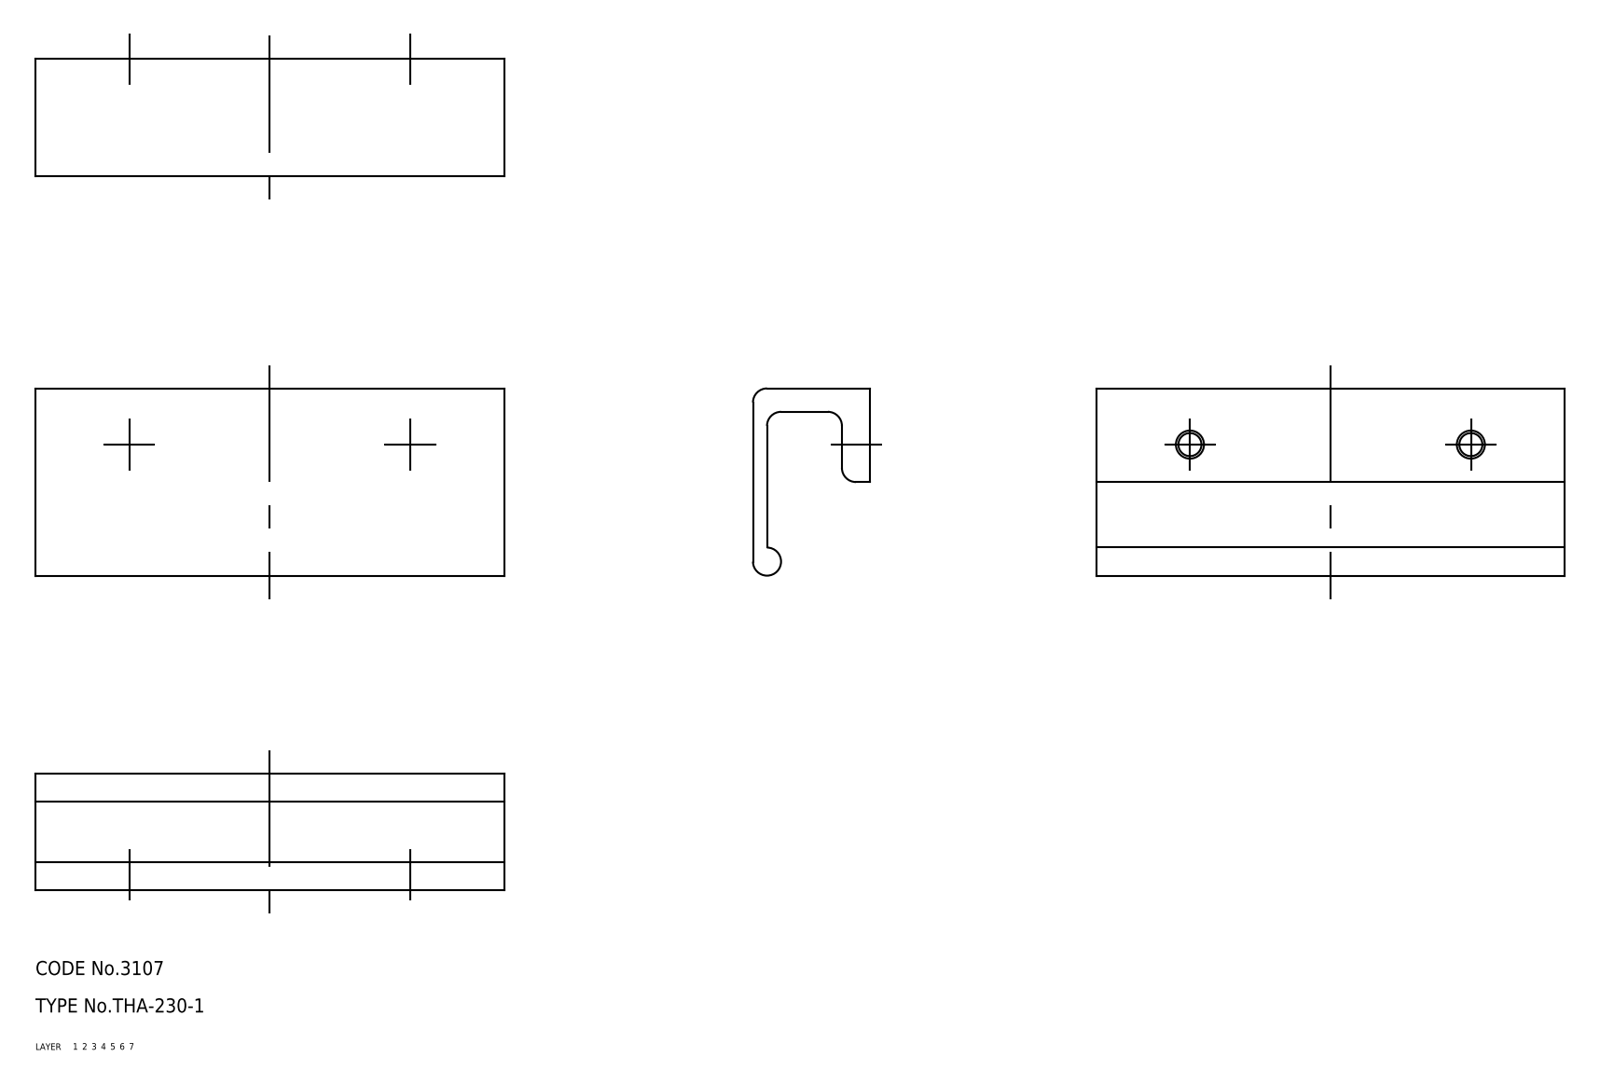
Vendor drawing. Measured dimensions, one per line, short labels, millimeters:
name: pull
written by: CADfix (AUTOMOTIVE_DESIGN)
unit: mm
bodies: 1 solid, 18 faces (0 planar, 0 cylindrical, 18 other)
size: 100 × 40 × 25
volume: 32 882 mm³; area: 16 476 mm²
